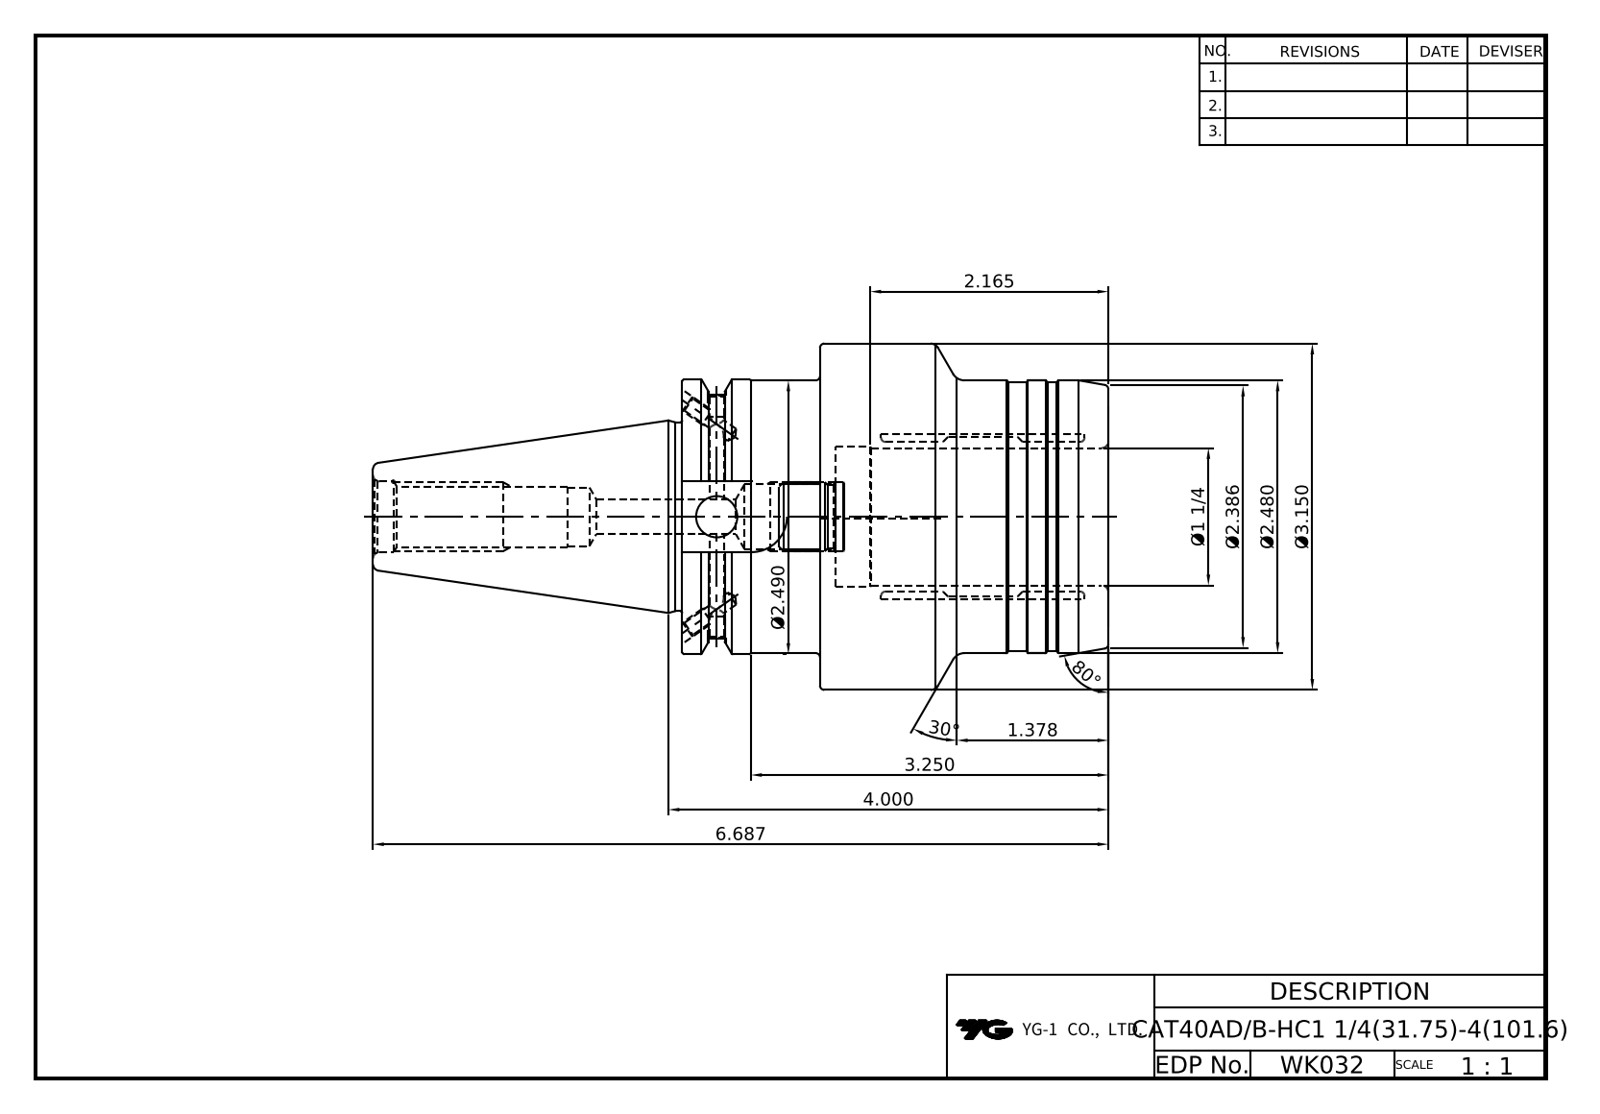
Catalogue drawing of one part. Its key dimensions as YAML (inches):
part_name: "WK032-CAT40ADB-HC1_25-4"
step_written_by: "PRO/ENGINEER BY PARAMETRIC TECHNOLOGY CORPORATION, 2012130 (CONFIG_CONTROL_DESIGN)"
units: inches
bodies: {solids: 1, faces: 198, planar: 34, cylindrical: 80, other: 84}
overall_size: [6.687, 3.15, 3.15]
volume: 21.9
surface_area: 77.01
round_holes:
  - {diameter: 0.13, count: 3}
  - {diameter: 0.138, count: 3}
  - {diameter: 0.157, count: 3}
  - {diameter: 0.165, count: 2}
  - {diameter: 0.315, count: 1}
  - {diameter: 0.375, count: 1}
  - {diameter: 0.531, count: 1}
  - {diameter: 0.551, count: 1}
  - {diameter: 0.594, count: 1}
  - {diameter: 0.642, count: 1}
  - {diameter: 1.25, count: 1}
  - {diameter: 1.276, count: 1}
round_bosses_or_shafts:
  - {diameter: 3.15, count: 1}
  - {diameter: 2.5, count: 1}
  - {diameter: 2.48, count: 1}
  - {diameter: 2.44, count: 1}
  - {diameter: 1.717, count: 1}
partial_cylinders:
  - {radius: 0.322, count: 1}
  - {radius: 1.108, count: 1}
face_to_face_distances: [2.622, 1.253, 3.875, 1.395, 0.142, 2.48, 1.795, 0.644, 0.239, 1.014]
